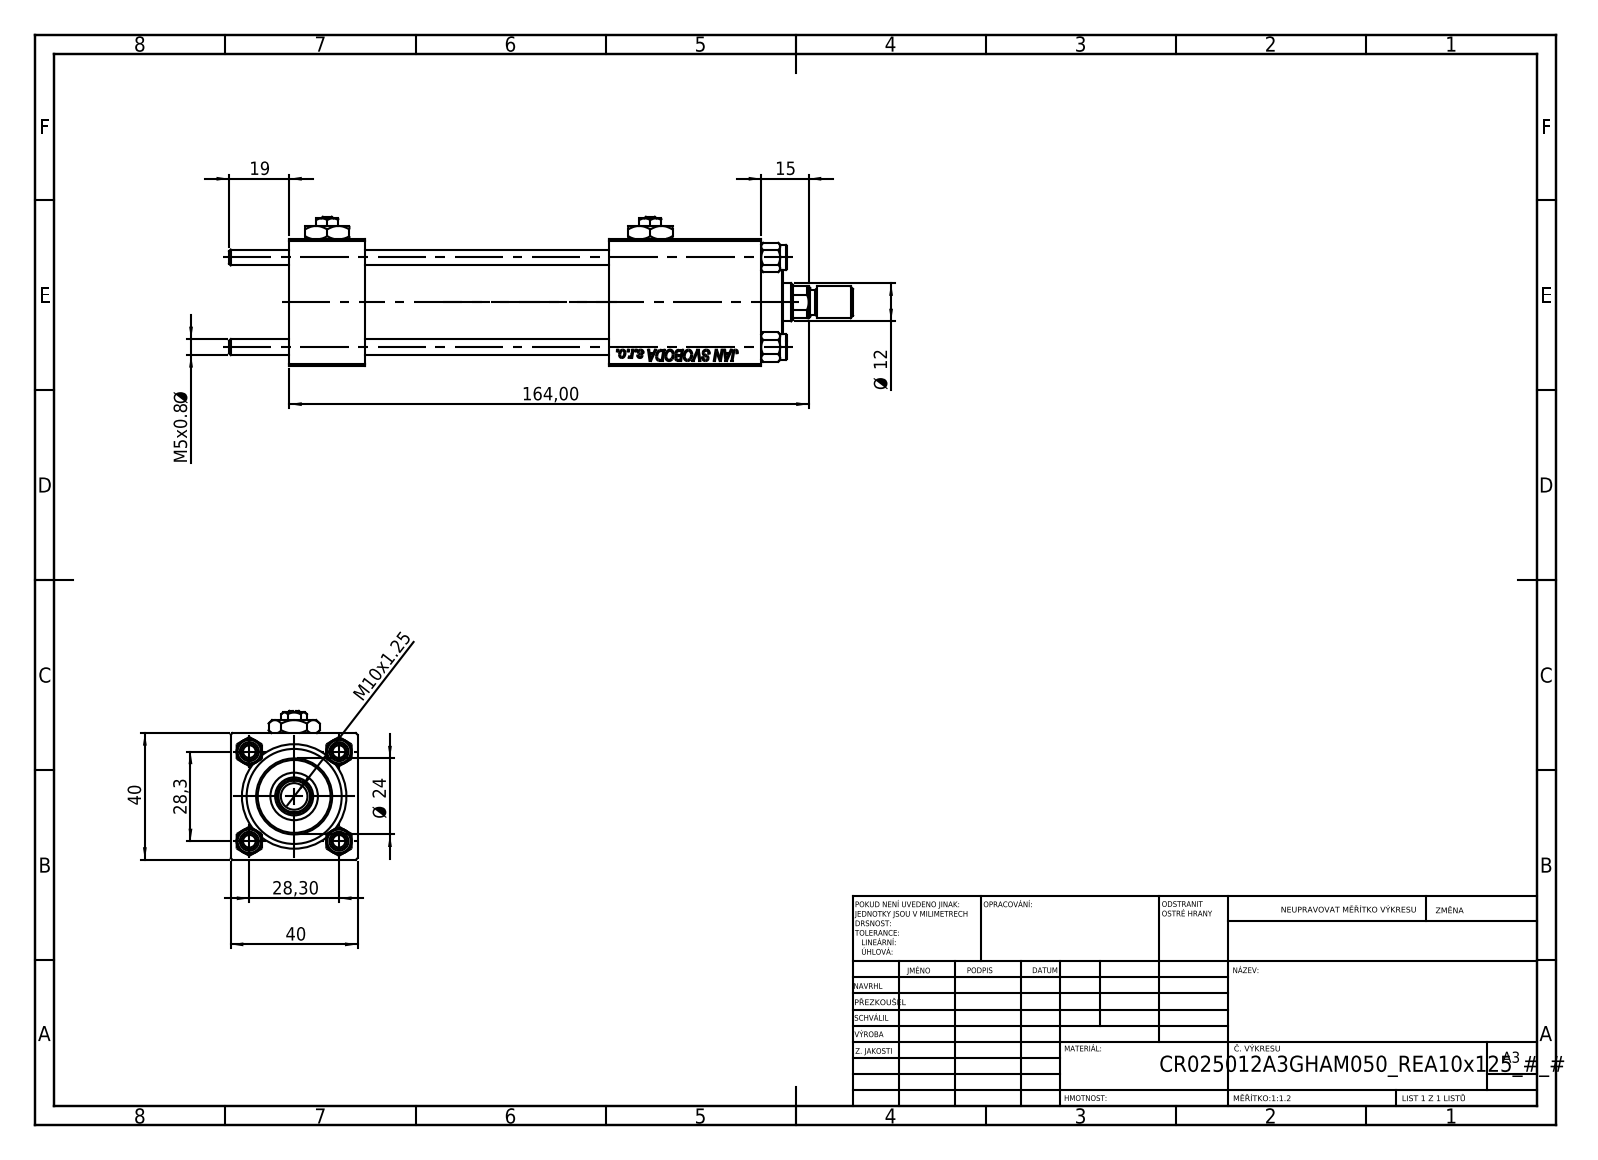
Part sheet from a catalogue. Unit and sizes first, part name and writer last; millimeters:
Units: millimetres
Overall size (bounding box): 197 × 47 × 40
Round holes (diameter × count): ⌀5 ×4, ⌀20 ×3, ⌀7 ×2, ⌀13.16 ×2, ⌀6.5 ×1, ⌀12 ×1, ⌀15 ×1, ⌀25 ×1, ⌀30 ×1
Round bosses / shafts (diameter × count): ⌀8 ×5, ⌀31 ×1, ⌀24 ×1, ⌀10 ×1
Partial cylindrical surfaces — rounded edges, fillets, slot ends (radius × count): R5.5 ×1
Main face-to-face distances: 40, 24, 39.8, 149, 125, 77, 120.3, 96.3, 28.7, 101
Hole centre spacings: 20.01, 28.3, 40.02, 102
Volume: 158 117 mm³ · Surface area: 69 543 mm²
Bodies: 14 solids, 1246 faces (568 planar, 94 cylindrical, 584 other)
Part name (STEP PRODUCT): ROD_END_AH; CR025_012_A_0_G_A_G_M_020_+#_##_TYCINKA; V215CR_VCP; NUT_M5 (+3 more)
STEP written by: SolidWorks 2019 (CONFIG_CONTROL_DESIGN)
